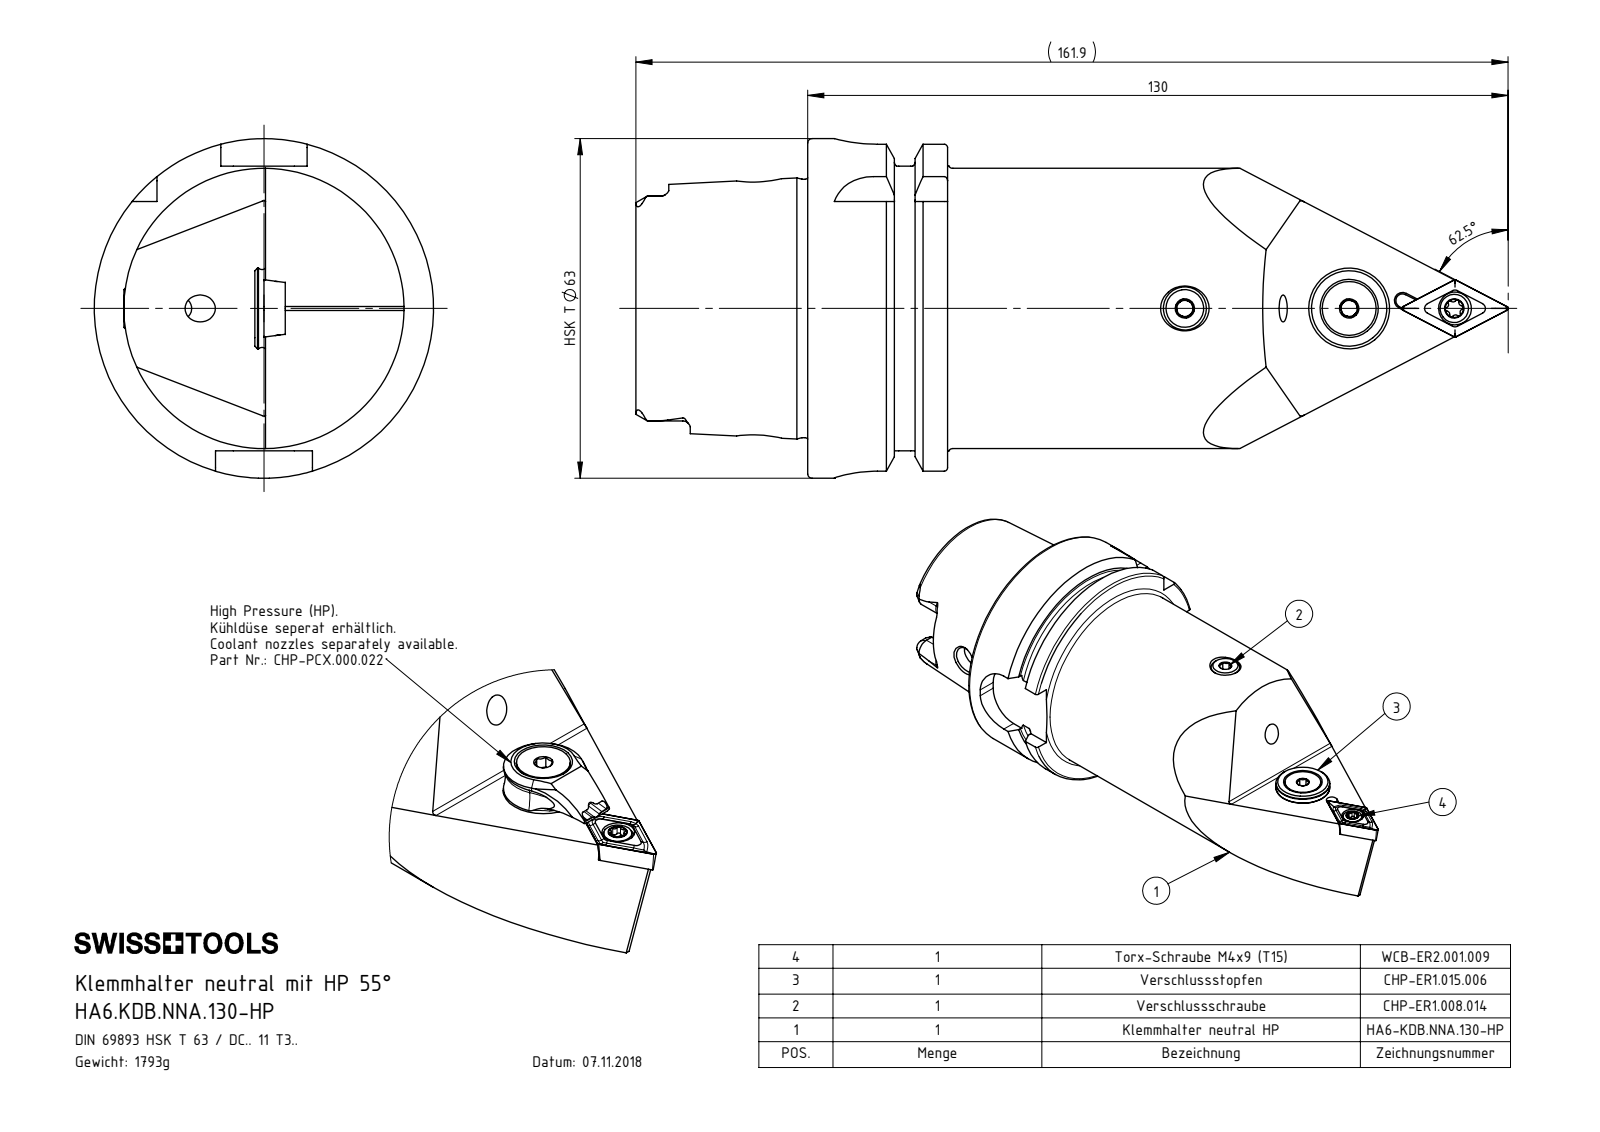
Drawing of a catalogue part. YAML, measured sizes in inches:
part_name: "DIN 7991 - M5x15; WCB-ER2.001.009_A; HA6-KDB.NNA.130-HP_E; CHP-ER1.008.014_A (+6 more)"
step_written_by: "SolidWorks 2017 (AUTOMOTIVE_DESIGN)"
units: inches
bodies: {solids: 8, faces: 421, planar: 116, cylindrical: 120, other: 185}
overall_size: [6.374, 2.48, 2.48]
volume: 13.92
surface_area: 61.14
round_holes:
  - {diameter: 0.197, count: 3}
  - {diameter: 0.165, count: 2}
  - {diameter: 0.047, count: 1}
  - {diameter: 0.079, count: 1}
  - {diameter: 0.098, count: 1}
  - {diameter: 0.118, count: 1}
  - {diameter: 0.13, count: 1}
  - {diameter: 0.173, count: 1}
  - {diameter: 0.205, count: 1}
  - {diameter: 0.24, count: 1}
  - {diameter: 0.276, count: 1}
  - {diameter: 0.295, count: 1}
round_bosses_or_shafts:
  - {diameter: 2.48, count: 1}
  - {diameter: 2.163, count: 1}
  - {diameter: 2.047, count: 1}
  - {diameter: 1.887, count: 1}
  - {diameter: 0.591, count: 1}
  - {diameter: 0.528, count: 1}
  - {diameter: 0.394, count: 1}
  - {diameter: 0.315, count: 1}
partial_cylinders:
  - {radius: 0.013, count: 6}
  - {radius: 0.023, count: 6}
  - {radius: 0.055, count: 6}
  - {radius: 0.113, count: 4}
  - {radius: 0.315, count: 4}
  - {radius: 0.031, count: 1}
  - {radius: 0.049, count: 1}
face_to_face_distances: [1.022, 0.63, 0.392, 1.256, 1.648, 2.278, 2.079, 0.858, 0.467, 0.177]
hole_center_spacings: [0.177, 0.641, 0.646, 0.769, 0.774, 1.201, 1.343, 1.969]
